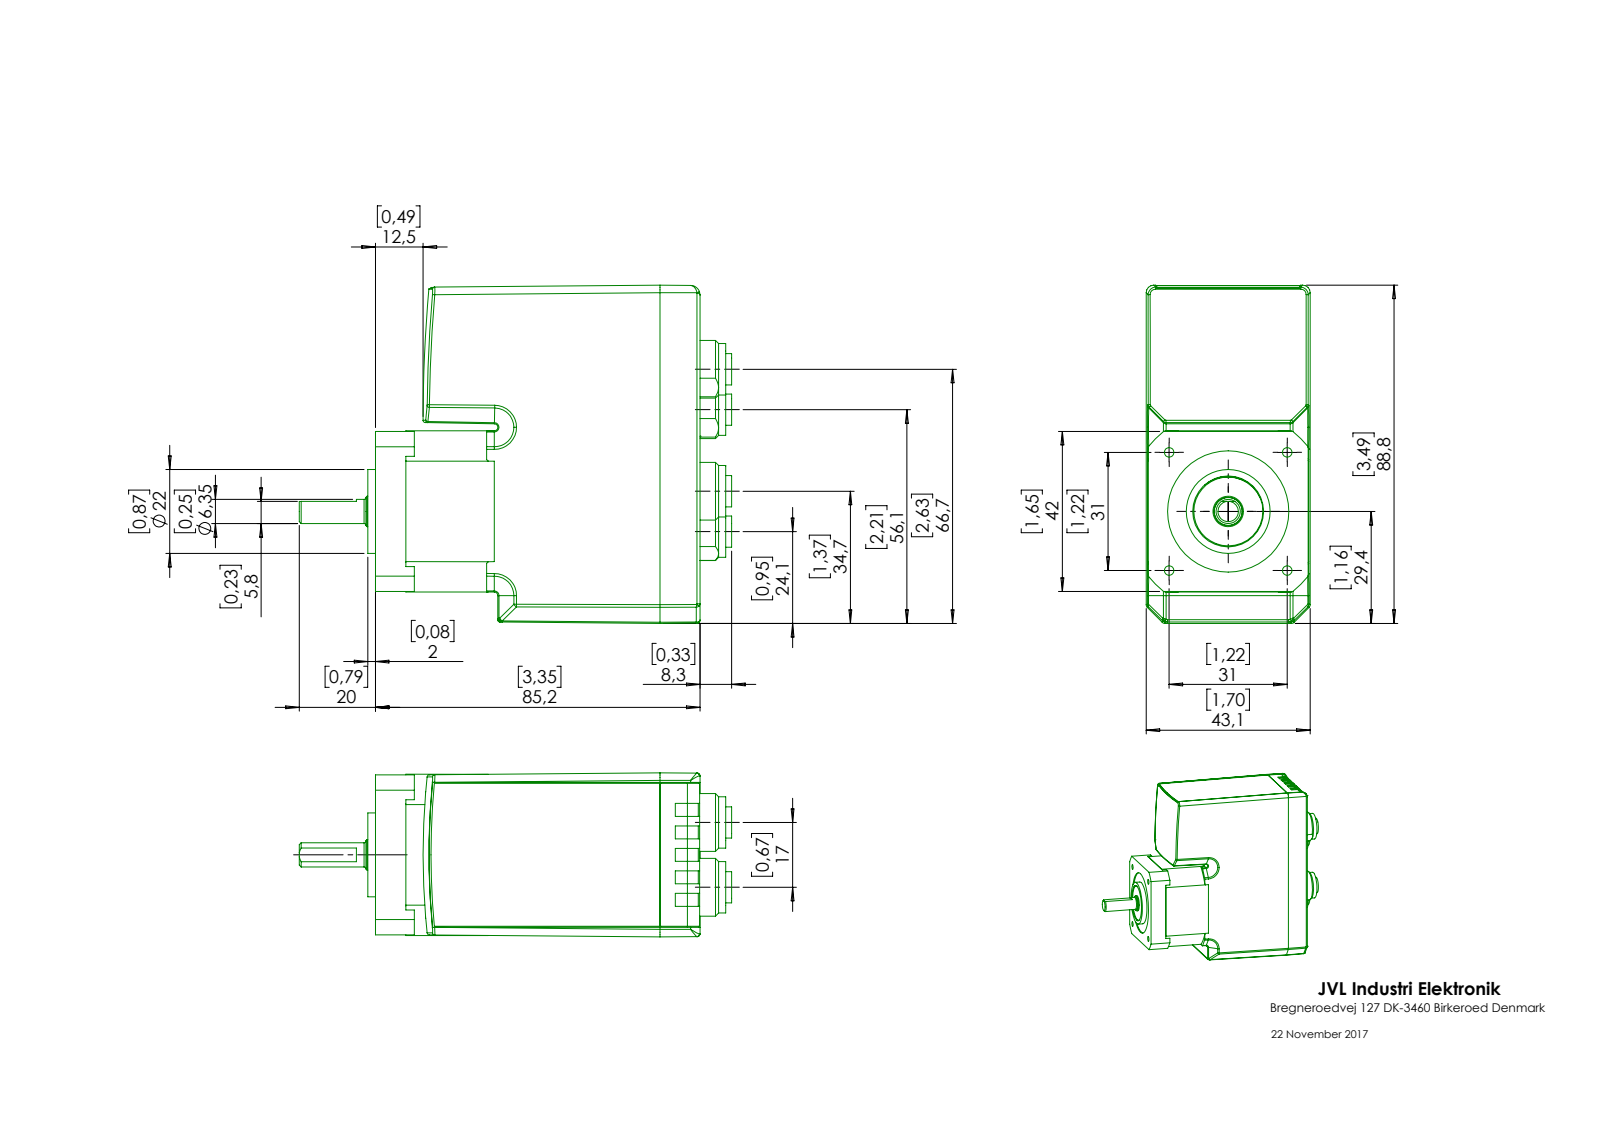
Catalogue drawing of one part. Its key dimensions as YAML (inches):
part_name: "MIS173 M12 END D635"
step_written_by: "SolidWorks 2017 (CONFIG_CONTROL_DESIGN)"
units: inches
bodies: {solids: 1, faces: 450, planar: 183, cylindrical: 150, other: 117}
overall_size: [4.469, 3.494, 1.695]
volume: 17.38
surface_area: 51.82
round_holes:
  - {diameter: 0.059, count: 5}
  - {diameter: 0.098, count: 4}
  - {diameter: 0.472, count: 4}
  - {diameter: 0.13, count: 1}
  - {diameter: 0.327, count: 1}
  - {diameter: 1.252, count: 1}
round_bosses_or_shafts:
  - {diameter: 0.596, count: 4}
  - {diameter: 0.531, count: 4}
  - {diameter: 0.323, count: 4}
  - {diameter: 0.866, count: 1}
  - {diameter: 0.315, count: 1}
  - {diameter: 0.295, count: 1}
  - {diameter: 0.25, count: 1}
partial_cylinders:
  - {radius: 0.039, count: 30}
  - {radius: 0.031, count: 3}
  - {radius: 0.037, count: 2}
  - {radius: 0.079, count: 2}
  - {radius: 0.15, count: 2}
  - {radius: 0.165, count: 2}
  - {radius: 0.014, count: 1}
  - {radius: 0.024, count: 1}
face_to_face_distances: [1.696, 1.665, 1.659, 3.35, 3.354, 1.654, 0.02, 3.331, 3.335, 0.014]
hole_center_spacings: [0.198, 0.754, 0.863, 1.024, 1.22, 1.256, 1.26, 1.608]
